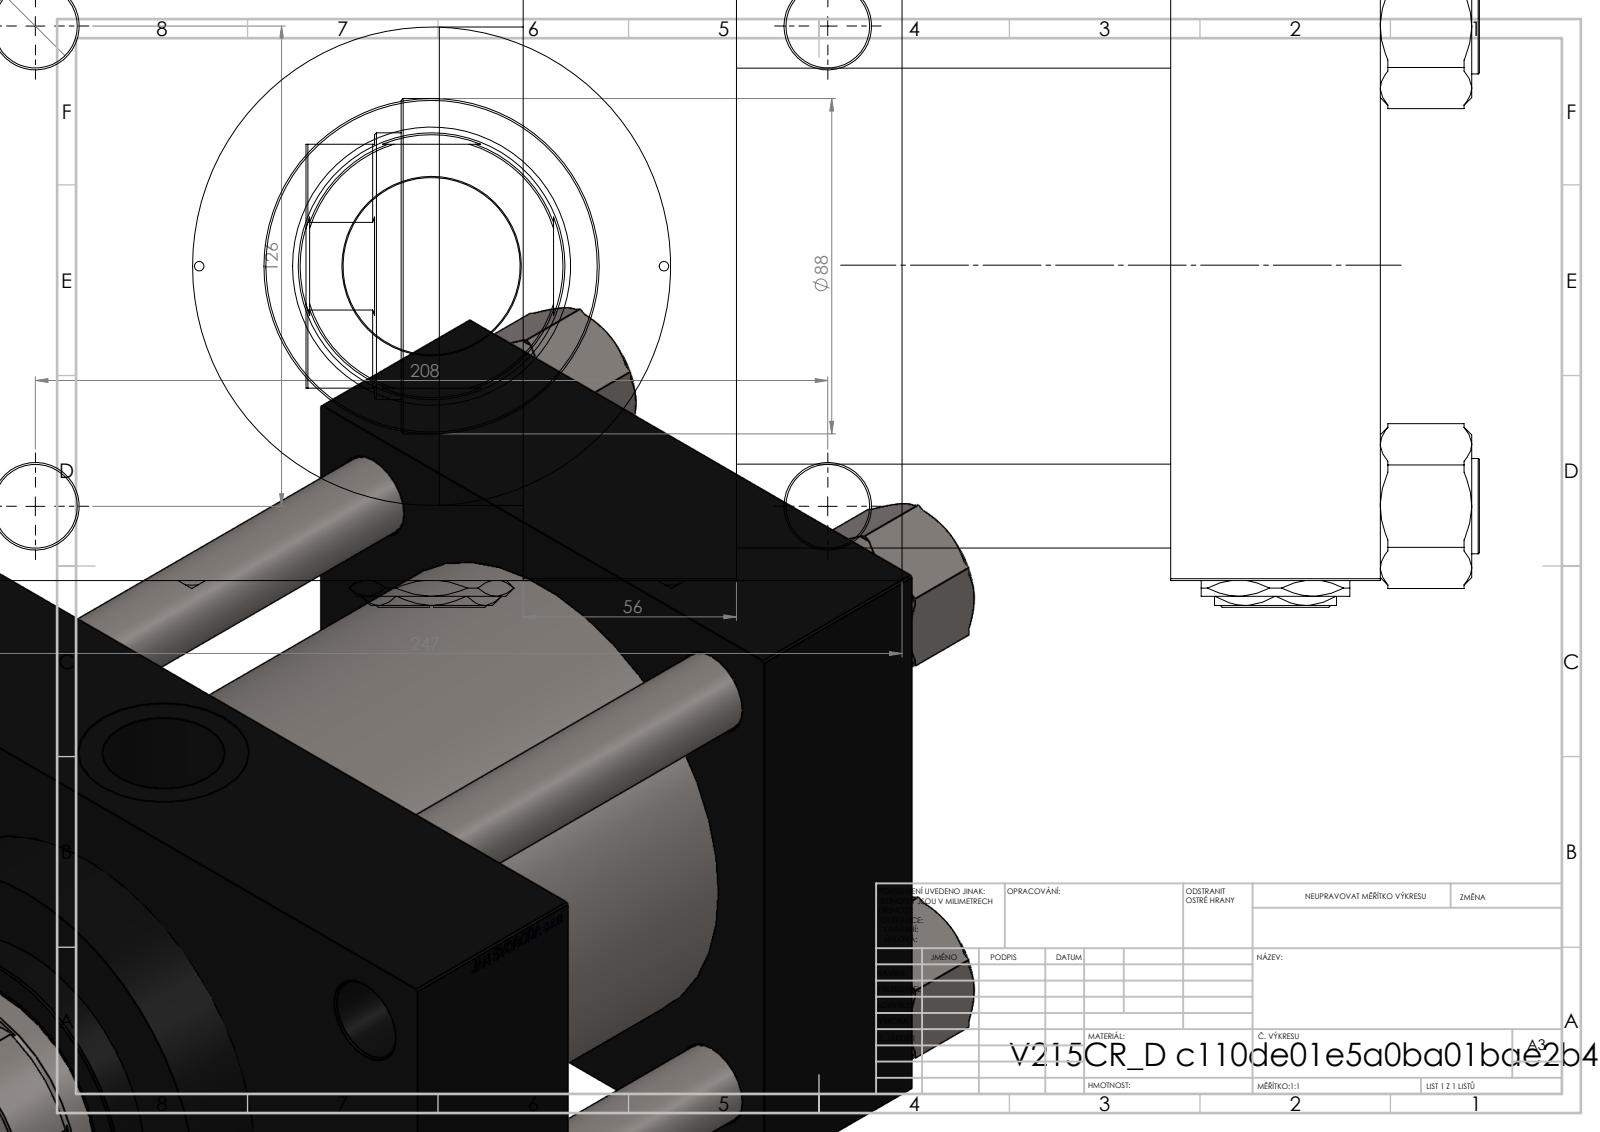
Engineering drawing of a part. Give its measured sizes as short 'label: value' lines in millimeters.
name: V215_VC_A; Zatka_pro_OIL_PORT; V215CR_D_TYCINKA; V215CR_D_Body (+2 more)
written by: SolidWorks 2019 (CONFIG_CONTROL_DESIGN)
unit: mm
bodies: 12 solids, 1197 faces (568 planar, 91 cylindrical, 538 other)
size: 308 × 247 × 174.07
volume: 5 252 000 mm³; area: 580 436 mm²
holes: 8× ⌀22, 2× ⌀2.5, 2× ⌀7, 2× ⌀32.24, 2× ⌀45, 1× ⌀46.5, 1× ⌀70, 1× ⌀73, 1× ⌀96, 1× ⌀125, 1× ⌀125.5
bosses: 4× ⌀25, 1× ⌀131, 1× ⌀88
rounds: 1× R34
face distances: 165, 114, 169, 55, 170, 56, 225, 41, 206, 247
hole spacings: 41.05, 62.98, 76.28, 89.02, 121.59, 125.9, 132.47, 139.02
